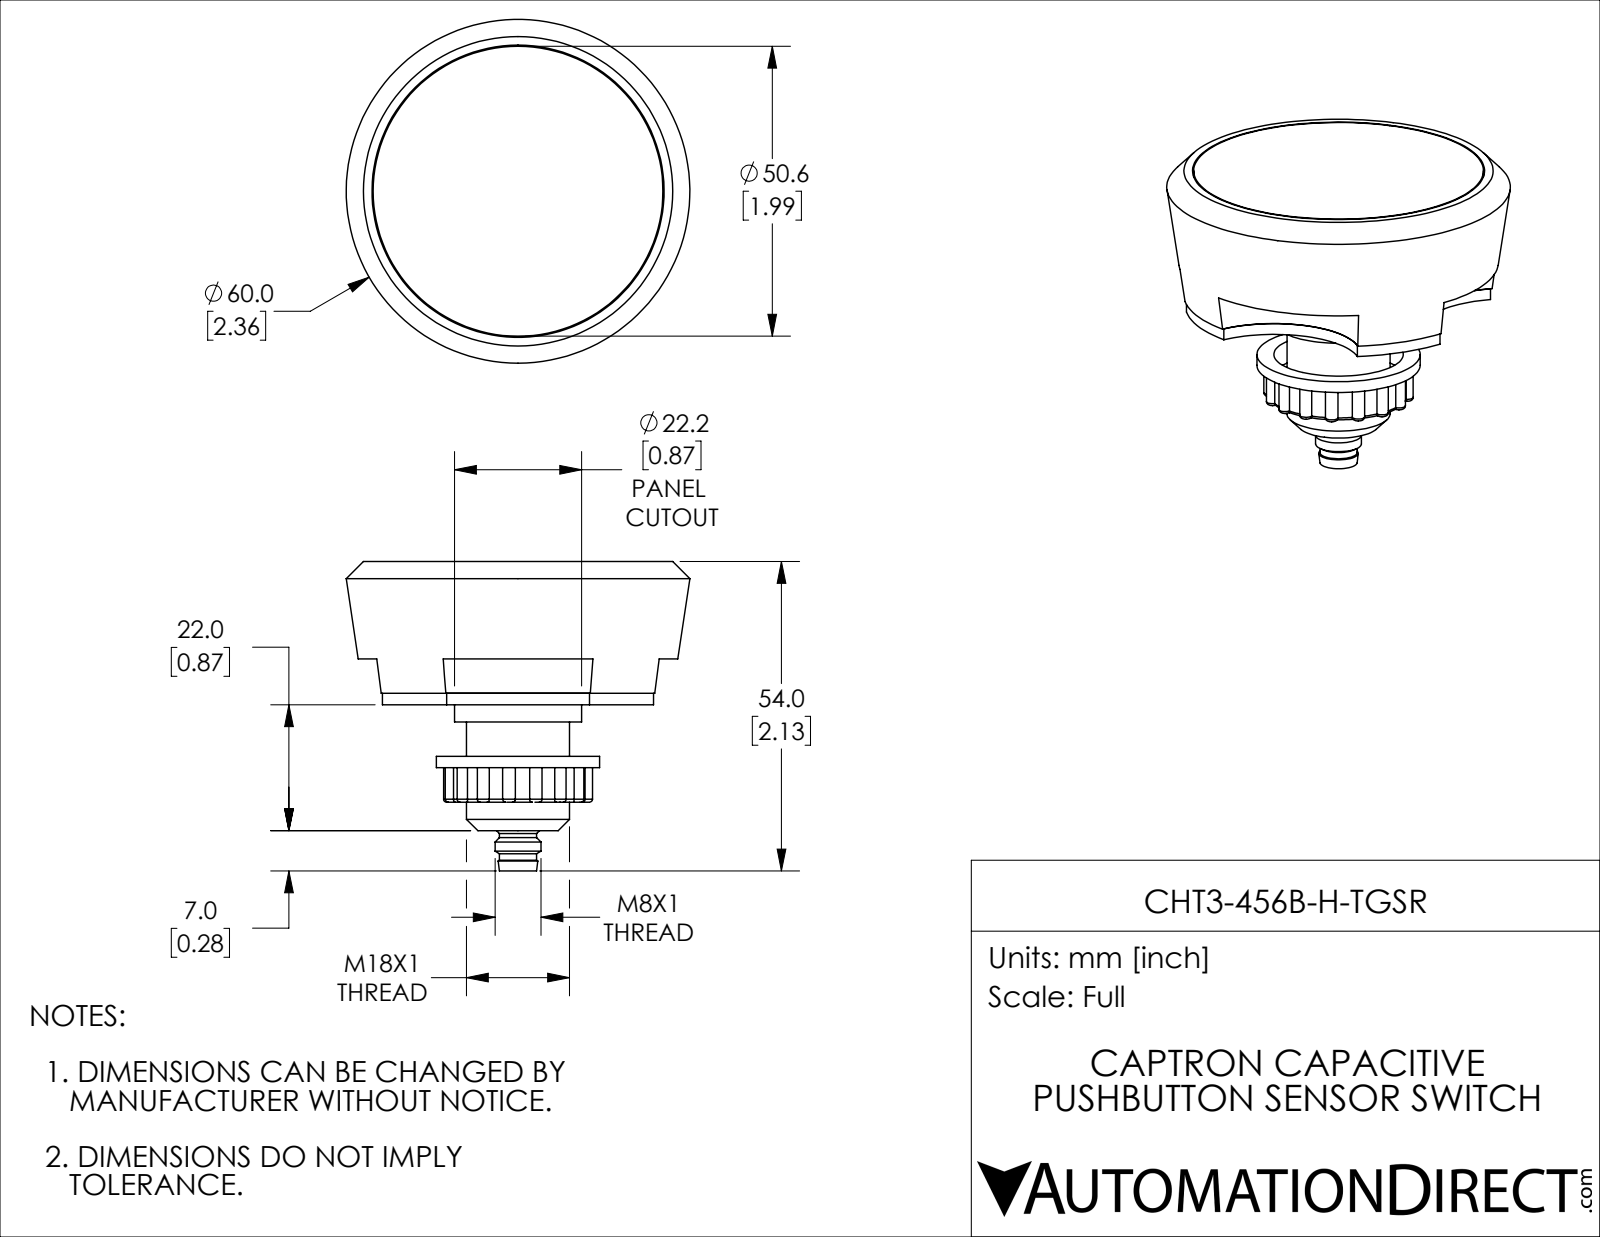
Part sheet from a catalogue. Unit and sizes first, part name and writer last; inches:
Units: inches
Overall size (bounding box): 2.362 × 2.362 × 2.126
Round holes (diameter × count): ⌀0.669 ×1, ⌀0.89 ×1, ⌀2.008 ×1
Round bosses / shafts (diameter × count): ⌀0.039 ×5, ⌀1.992 ×1, ⌀1.122 ×1, ⌀0.874 ×1, ⌀0.709 ×1, ⌀0.315 ×1, ⌀0.256 ×1
Partial cylindrical surfaces — rounded edges, fillets, slot ends (radius × count): R0.043 ×16, R0.591 ×4, R0.02 ×2, R0.039 ×1, R0.114 ×1, R0.472 ×1, R1.053 ×1
Main face-to-face distances: 0.906, 0.091, 0.815, 0.134, 0.772, 0.043, 0.079, 0.984, 0.669, 0.85
Volume: 3.853 in³ · Surface area: 32.45 in²
Bodies: 10 solids, 200 faces (28 planar, 94 cylindrical, 78 other)
Part name (STEP PRODUCT): CHT3-456B-H-TGSR
STEP written by: SolidWorks 2019 (CONFIG_CONTROL_DESIGN)
